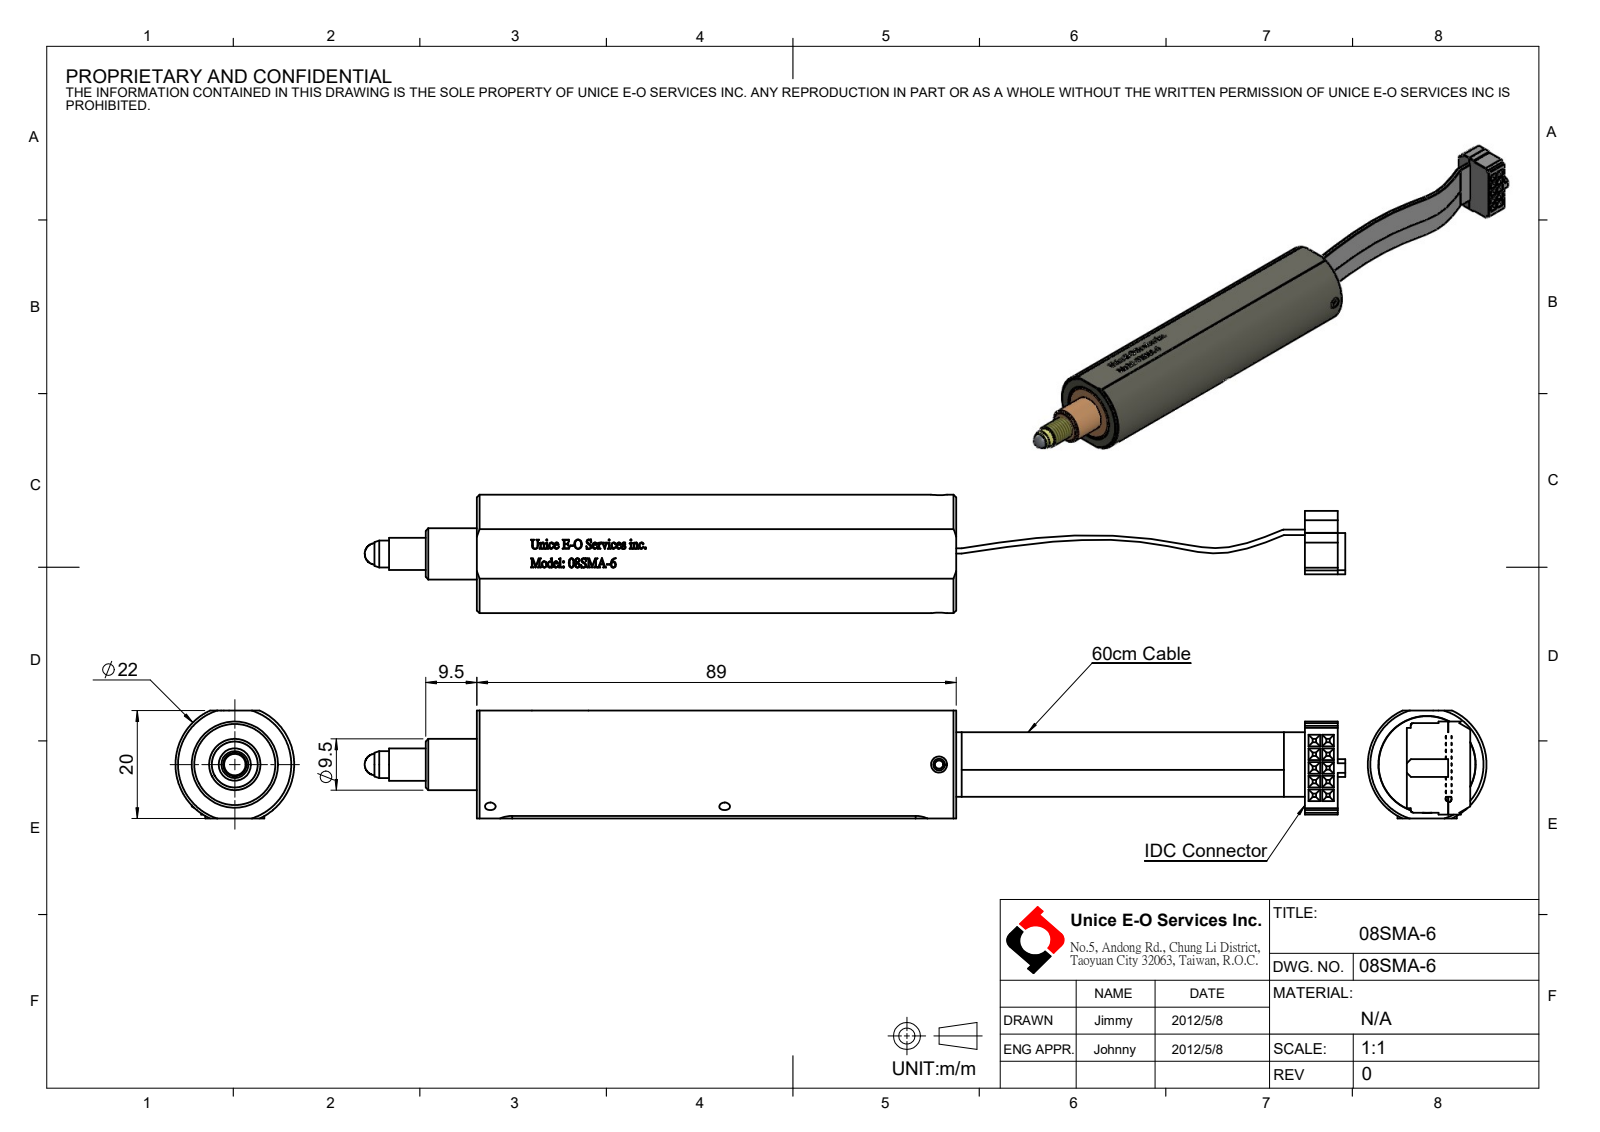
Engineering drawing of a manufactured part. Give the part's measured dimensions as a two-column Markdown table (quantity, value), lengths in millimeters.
| quantity | value |
| --- | --- |
| part name | 08SMA-6 |
| STEP written by | SolidWorks 2016 (CONFIG_CONTROL_DESIGN) |
| units | millimeters |
| bodies | 20 solids, 1510 faces (735 planar, 237 cylindrical, 538 other) |
| overall size | 181.99 × 22 × 20 |
| volume | 27 248 mm³ |
| surface area | 25 428 mm² |
| round holes (diameter × count) | 1.6 × 9, 2 × 5, 2.05 × 4, 2.2 × 3, 3 × 3, 1.48 × 2, 1.7 × 1, 4 × 1, 5.1 × 1, 7.2 × 1, 10 × 1, 18 × 1 |
| round bosses / shafts (diameter × count) | 1.8 × 8, 16 × 1, 15.5 × 1, 15 × 1, 14.8 × 1, 12 × 1, 9.5 × 1, 9 × 1 |
| partial cylindrical surfaces (radius × count) | 0.48 × 10, 0.64 × 10, 1.1 × 8, 3 × 8, 0.51 × 2, 0.75 × 2, 1 × 2, 1.05 × 2 |
| main face-to-face distances | 0.8, 20, 19.2, 18.4, 2, 0.5, 1.6, 1, 23.1, 44.5 |
| hole center spacings | 5.5, 7.78, 7, 3.78, 4.61, 5.46, 9, 9.66 |
